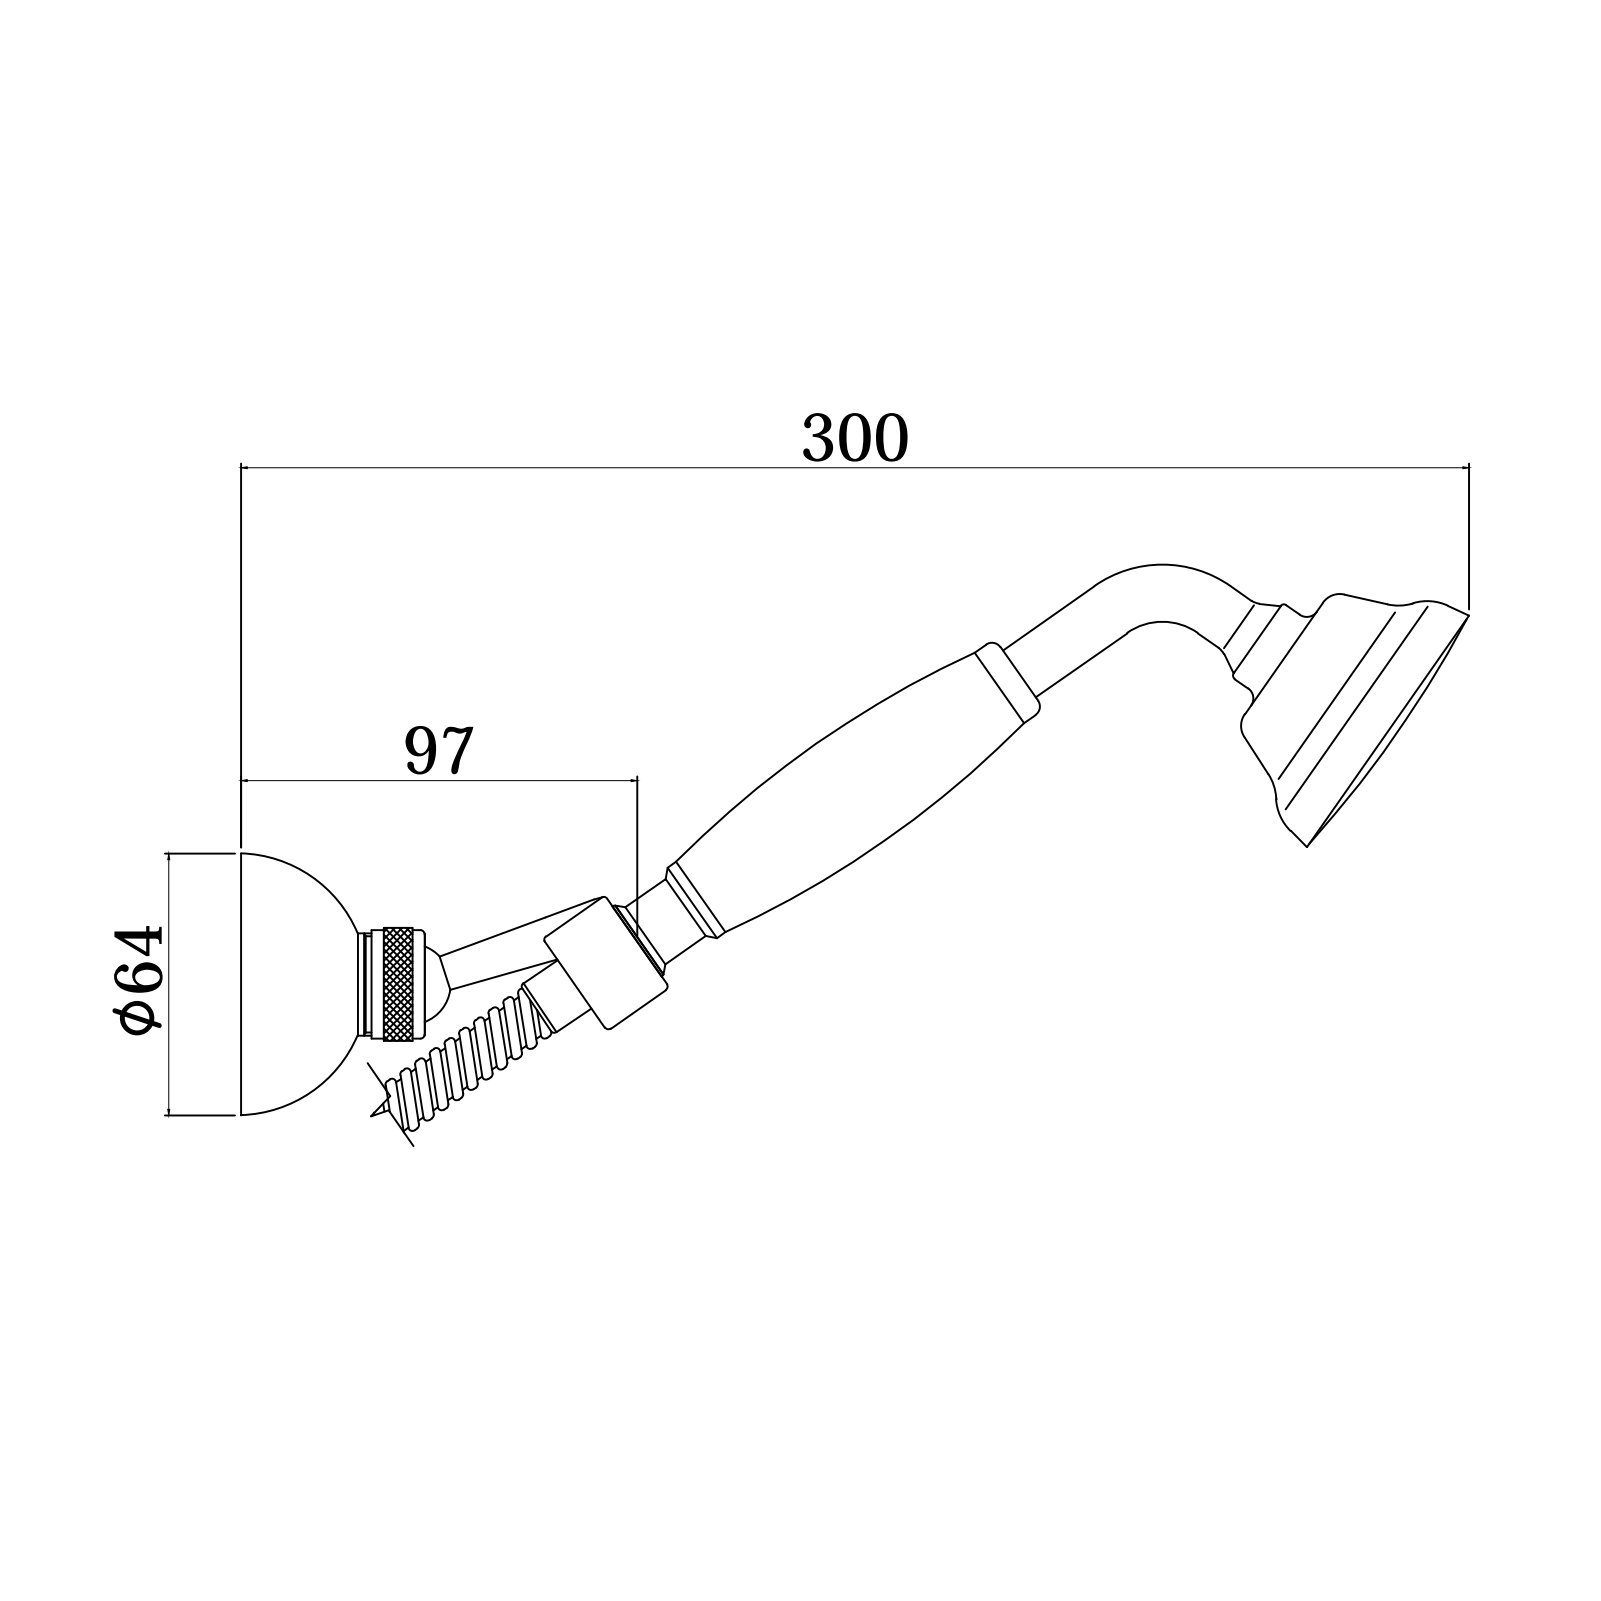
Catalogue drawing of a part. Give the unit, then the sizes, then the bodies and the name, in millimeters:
Units: millimetres
Overall size (bounding box): 281.51 × 218.38 × 69
Round holes (diameter × count): ⌀1.2 ×45, ⌀12.2 ×2, ⌀14.5 ×2, ⌀6 ×1, ⌀10 ×1, ⌀10.5 ×1, ⌀13 ×1, ⌀14.7 ×1, ⌀15.4 ×1, ⌀18 ×1, ⌀18.7 ×1, ⌀19 ×1
Round bosses / shafts (diameter × count): ⌀21 ×2, ⌀20.5 ×2, ⌀14 ×2, ⌀69 ×1, ⌀29 ×1, ⌀27 ×1, ⌀26 ×1, ⌀24.5 ×1
Partial cylindrical surfaces — rounded edges, fillets, slot ends (radius × count): R0.5 ×14, R5.25 ×1, R10 ×1
Main face-to-face distances: 2, 1.5, 27.5, 3.5, 31, 11.5, 25.5, 5, 15.5, 5.5
Hole centre spacings: 24, 14, 17.23, 19, 12.42, 18.37, 6.26, 11.09
Volume: 128 004 mm³ · Surface area: 77 199 mm²
Bodies: 2 solids, 545 faces (89 planar, 196 cylindrical, 260 other)
Part name (STEP PRODUCT): ZDUP035CR
STEP written by: CREO PARAMETRIC BY PTC INC, 2020044 (CONFIG_CONTROL_DESIGN)
